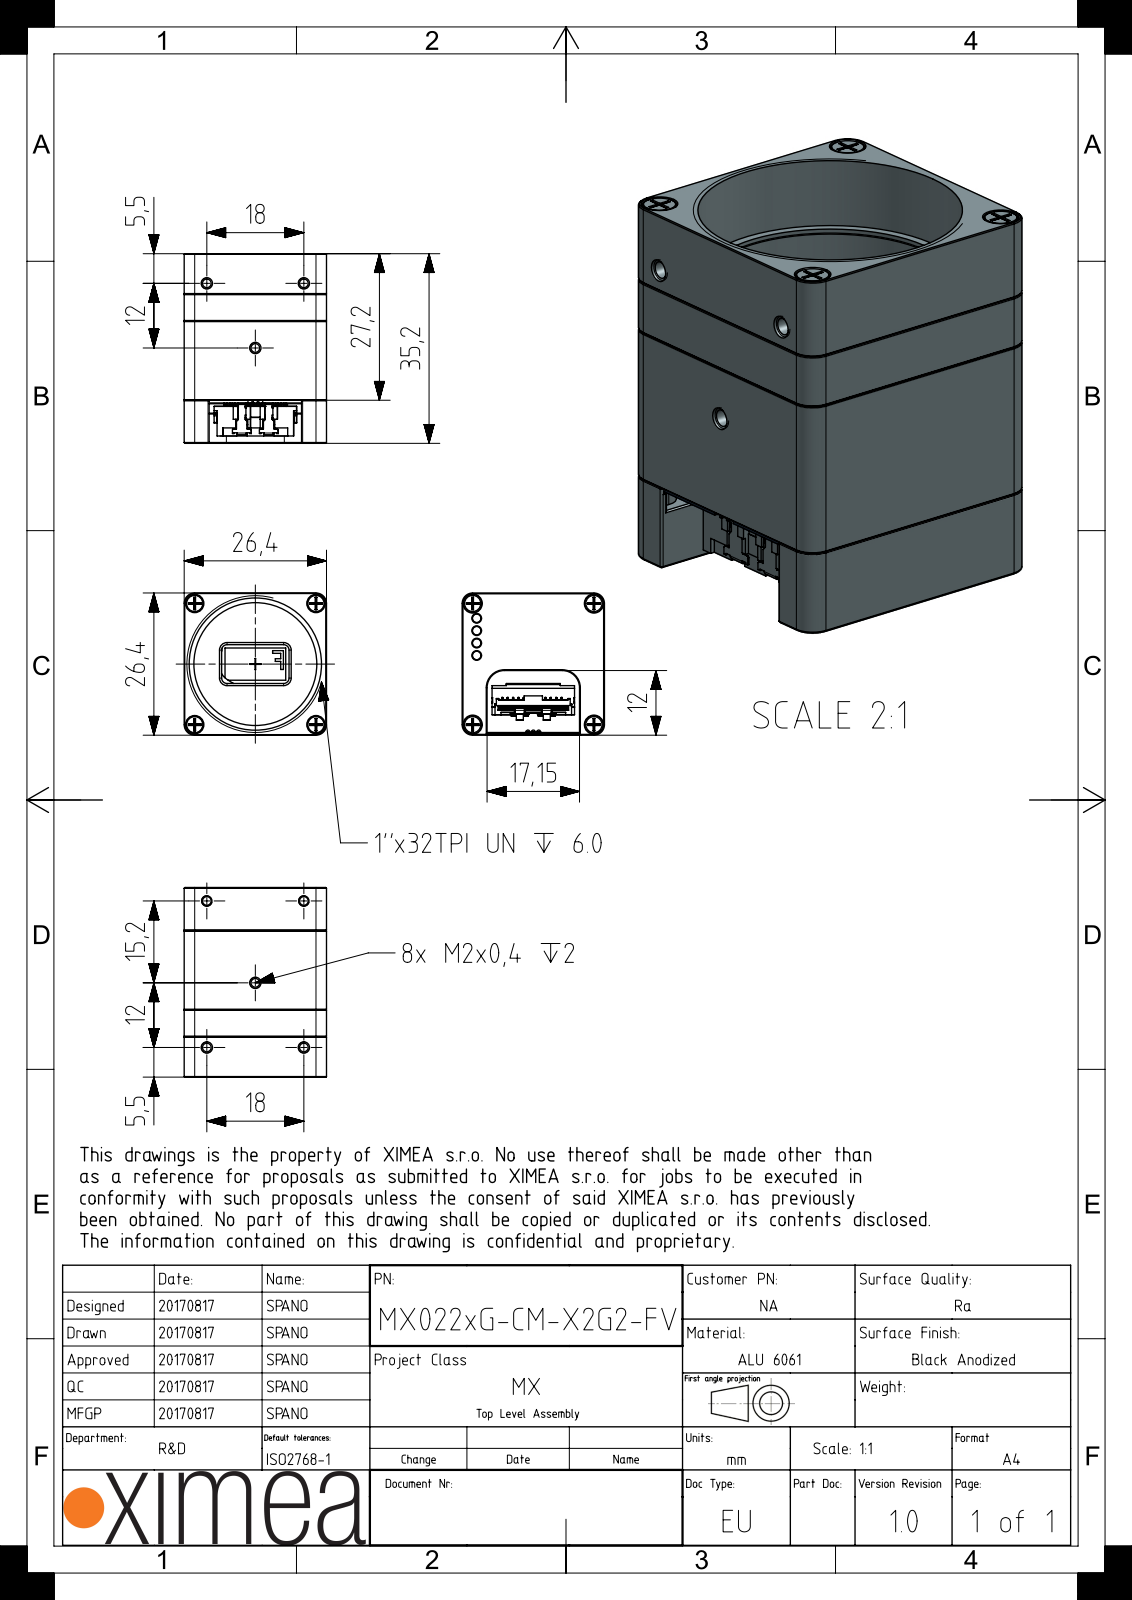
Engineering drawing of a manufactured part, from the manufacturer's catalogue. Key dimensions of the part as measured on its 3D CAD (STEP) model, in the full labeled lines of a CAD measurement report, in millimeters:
Part name (STEP PRODUCT): CMV2000_Glass; CMV2000_Package; SROB-M2x10-CUST; MECH-MX-THERMAL-PAD-10X10 (+8 more)
STEP written by: SIEMENS PLM Software NX 1907 (AUTOMOTIVE_DESIGN)
Units: millimetres
Bodies: 135 solids, 7941 faces (5329 planar, 2240 cylindrical, 372 other)
Overall size (bounding box): 35.2 × 26.4 × 26.4
Volume: 11 500 mm³ · Surface area: 19 700 mm²
Round holes (diameter × count): ⌀0.8 ×95, ⌀1.6 ×13, ⌀0.5 ×5, ⌀0.9 ×4, ⌀1.8 ×4, ⌀2 ×4, ⌀2.1 ×4, ⌀3 ×4, ⌀3.2 ×4, ⌀3.4 ×4, ⌀1.3 ×2, ⌀21 ×1
Round bosses / shafts (diameter × count): ⌀0.3 ×95, ⌀1.9 ×4, ⌀1.6 ×4, ⌀0.8 ×4, ⌀3 ×2, ⌀1.6 ×2, ⌀25 ×1, ⌀21.6 ×1
Partial cylindrical surfaces — rounded edges, fillets, slot ends (radius × count): R1 ×20, R1.5 ×19, R0.4 ×18, R0.3 ×16, R1.3 ×16, R0.2 ×14, R0.2 ×9, R0.1 ×8
Main face-to-face distances: 1, 26.4, 3.6, 11.1, 7.7, 15.8, 14.8, 14.7, 4.6, 11.2
Hole centre spacings: 1.3, 2.8, 1.8, 2.5, 4, 5.2, 3.8, 6.5
